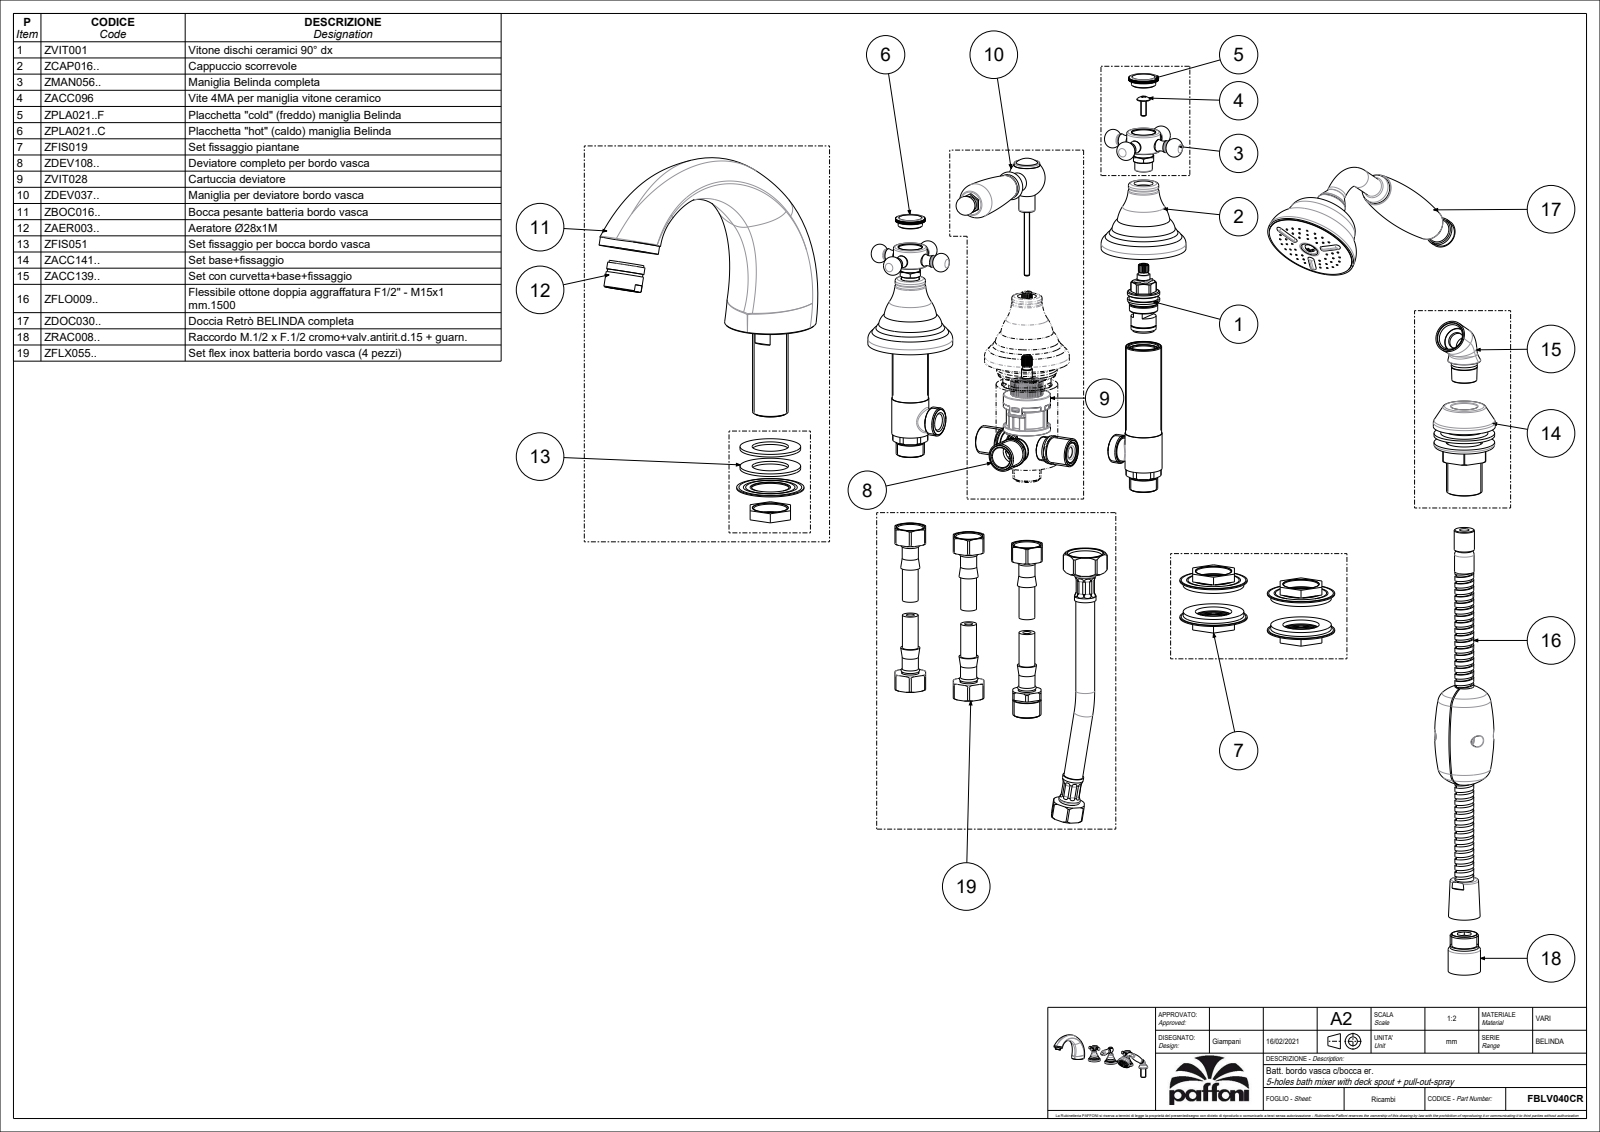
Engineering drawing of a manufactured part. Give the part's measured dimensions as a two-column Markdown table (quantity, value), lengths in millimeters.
| quantity | value |
| --- | --- |
| part name | FBLV040CR |
| STEP written by | CREO PARAMETRIC BY PTC INC, 2020044 (CONFIG_CONTROL_DESIGN) |
| units | millimeters |
| bodies | 5 solids, 1298 faces (479 planar, 400 cylindrical, 419 other) |
| overall size | 468.5 × 267.6 × 150.84 |
| volume | 1 010 000 mm³ |
| surface area | 138 306 mm² |
| round holes (diameter × count) | 1.2 × 45 |
| round bosses / shafts (diameter × count) | 14 × 5, 63 × 3, 22.5 × 3, 9 × 3, 7 × 3, 25 × 2, 13 × 2, 69 × 1 |
| partial cylindrical surfaces (radius × count) | 11 × 2 |
| main face-to-face distances | 60.4, 10, 50, 10.4, 15.7, 34.3, 44.7, 31.01, 15, 14 |
| hole center spacings | 12.42, 13.78, 17.23, 20.88, 18.37, 33.28, 37.69, 6.26 |
